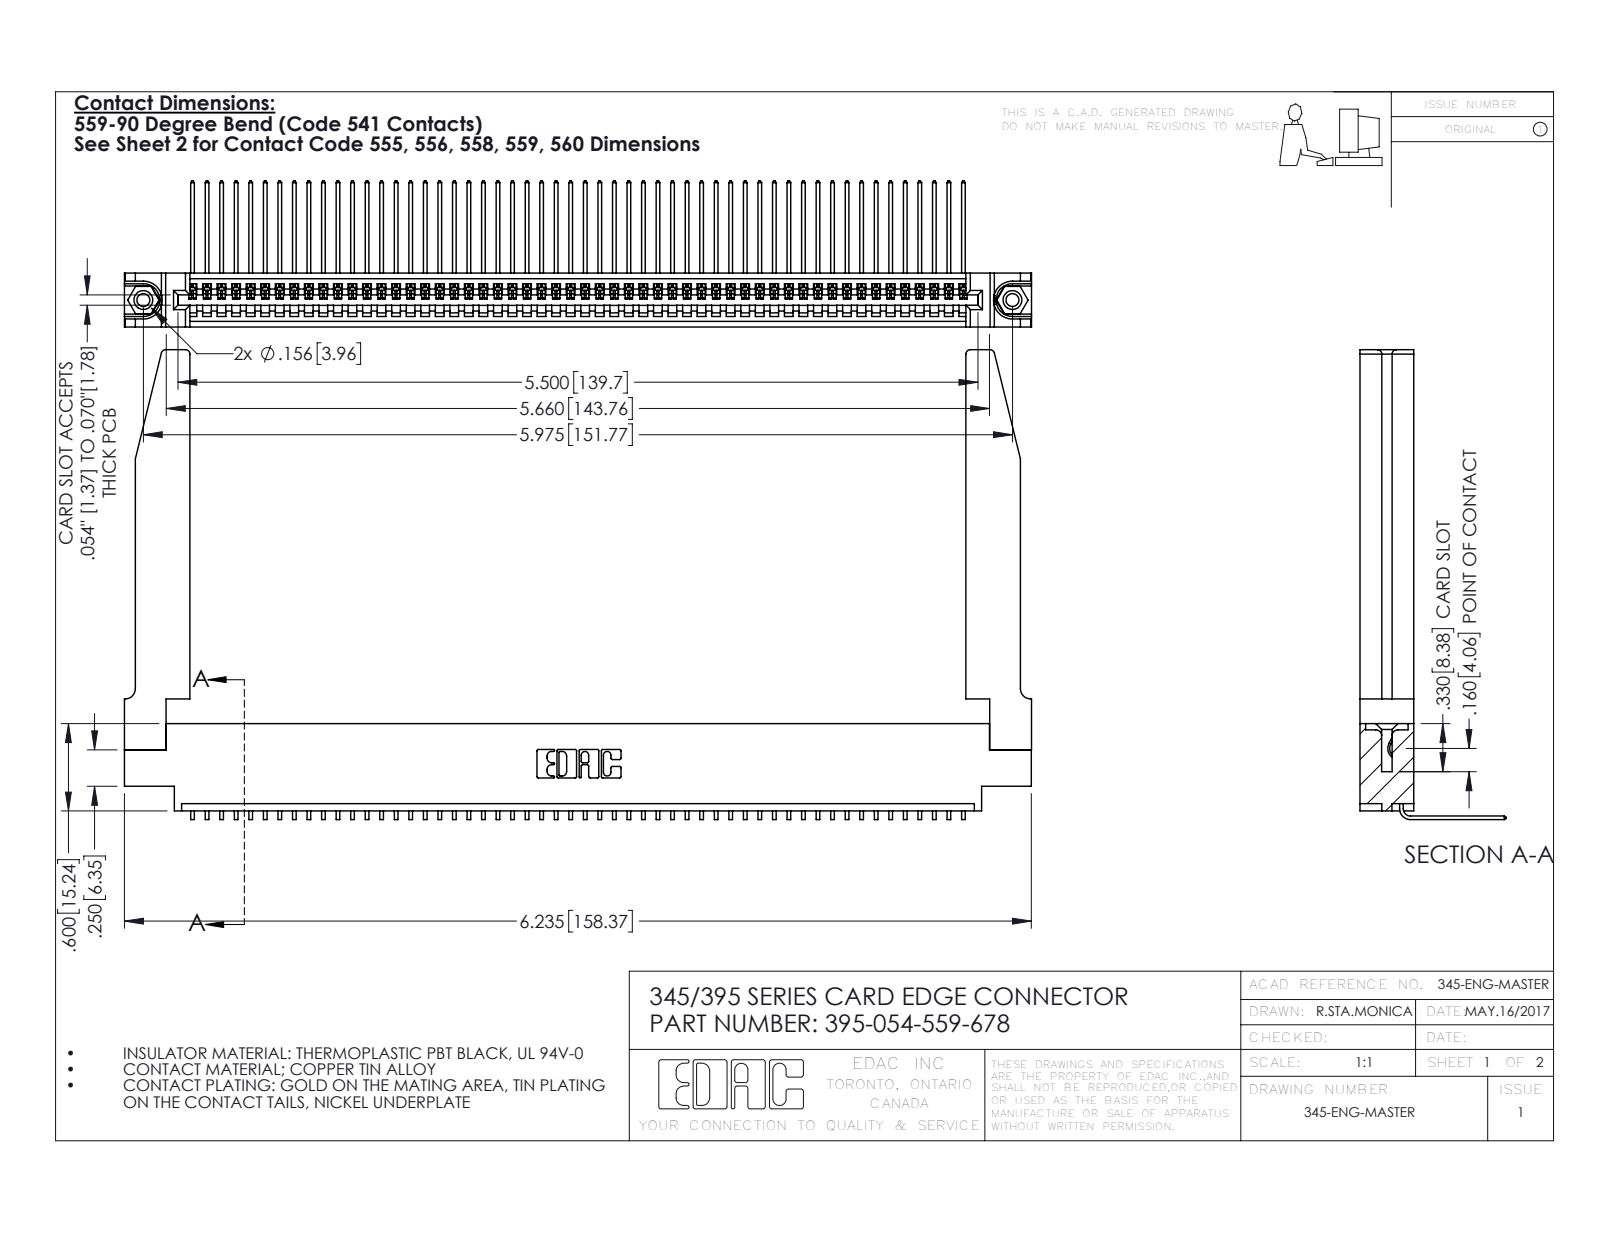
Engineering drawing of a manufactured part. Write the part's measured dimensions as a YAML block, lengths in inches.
part_name: "345-292-001_558 559 Tail - 1; 345-250-001_345-250-001-102; 345-220-078_345-220-078; 395-054-559-678 (+1 more)"
step_written_by: "SolidWorks 2016 (CONFIG_CONTROL_DESIGN)"
units: inches
bodies: {solids: 59, faces: 3604, planar: 2494, cylindrical: 1058, other: 52}
overall_size: [6.236, 3.229, 1.005]
volume: 1.402
surface_area: 44.03
round_holes:
  - {diameter: 0.089, count: 2}
  - {diameter: 0.125, count: 2}
  - {diameter: 0.156, count: 2}
  - {diameter: 0.064, count: 1}
round_bosses_or_shafts:
  - {diameter: 0.155, count: 2}
partial_cylinders:
  - {radius: 0.006, count: 108}
  - {radius: 0.01, count: 22}
  - {radius: 0.03, count: 8}
  - {radius: 0.007, count: 6}
  - {radius: 0.031, count: 6}
  - {radius: 0.026, count: 3}
  - {radius: 0.031, count: 2}
  - {radius: 0.04, count: 2}
face_to_face_distances: [0.37, 0.072, 0.298, 0.098, 0.272, 0.025, 0.2, 0.225, 0.148, 0.15]
hole_center_spacings: [0.27, 5.739, 5.975]
